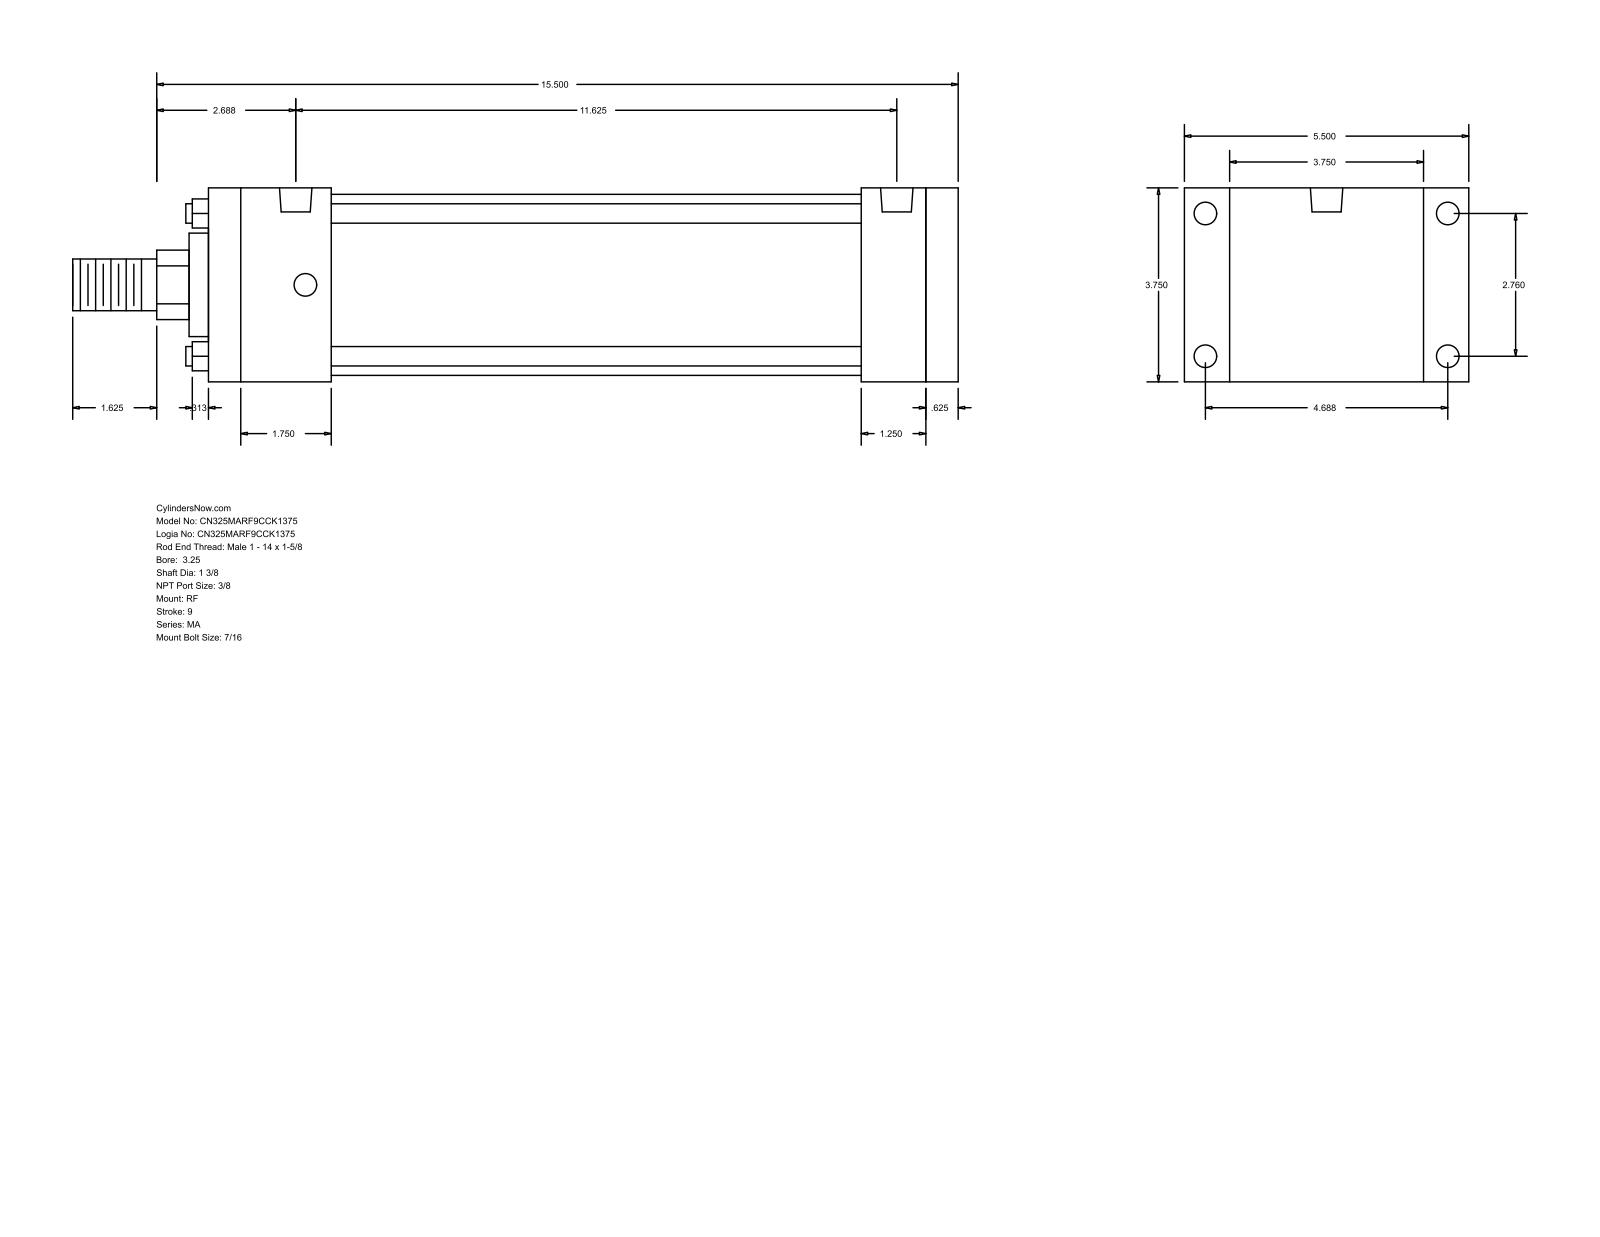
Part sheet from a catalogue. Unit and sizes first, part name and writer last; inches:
Units: inches
Overall size (bounding box): 17.125 × 5.5 × 3.75
Round holes (diameter × count): ⌀0.437 ×8, ⌀0.627 ×2
Round bosses / shafts (diameter × count): ⌀0.375 ×4, ⌀3.5 ×1, ⌀2 ×1, ⌀1.375 ×1, ⌀1 ×1
Partial cylindrical surfaces — rounded edges, fillets, slot ends (radius × count): R0.672 ×1
Main face-to-face distances: 3.75, 14.5, 0.625, 13.875, 0.875, 4.625, 12.625, 1.25, 1.875, 2.375
Hole centre spacings: 0.188, 2.76, 4.687, 5.439, 11.25, 11.437, 11.625
Bodies: 0 solids, 92 faces (64 planar, 28 cylindrical, 0 other)
Part name (STEP PRODUCT): MA_RF__0325_1.375
STEP written by: GSSL Pune (CONFIG_CONTROL_DESIGN)
